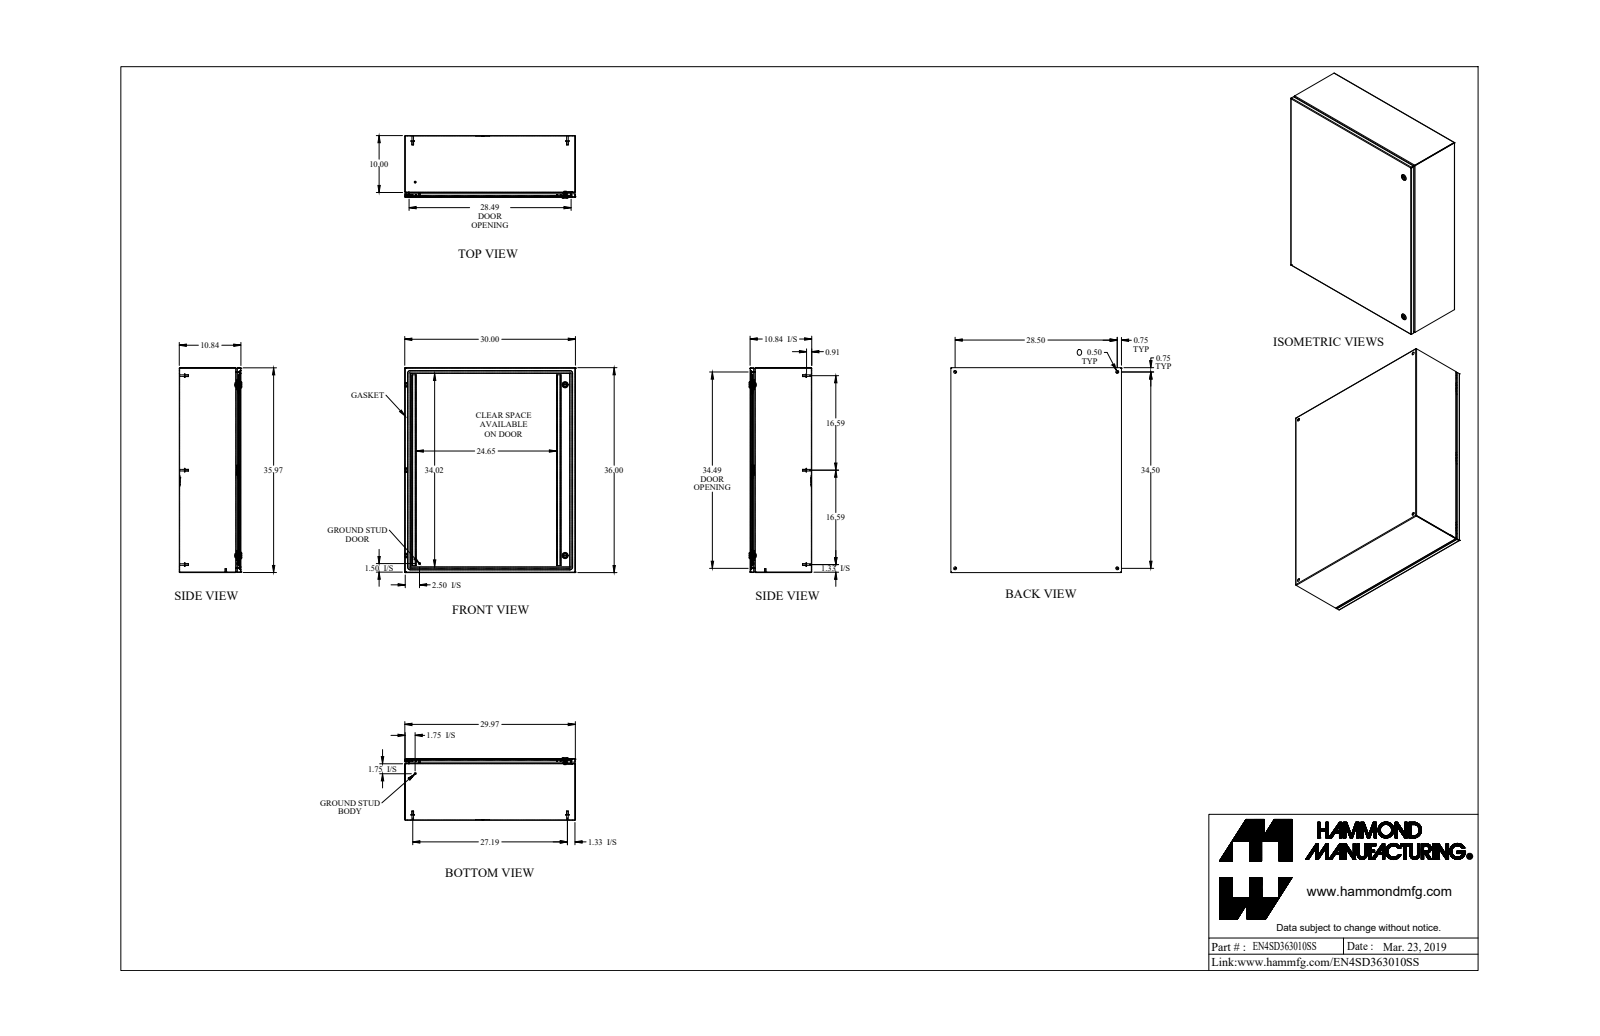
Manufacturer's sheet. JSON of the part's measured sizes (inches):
{"part_name": "EN4SD363010SS", "step_written_by": "SolidWorks 2019 (AUTOMOTIVE_DESIGN)", "units": "inches", "bodies": {"solids": 35, "faces": 959, "planar": 458, "cylindrical": 313, "other": 188}, "overall_size": [36, 30, 11.002], "volume_in3": 286.6, "surface_area_in2": 8035, "round_holes": [[0.5, 6], [0.197, 2], [0.387, 2], [0.63, 2], [0.768, 2], [0.172, 1], [0.24, 1], [0.242, 1]], "round_bosses_or_shafts": [[0.313, 8], [0.275, 6], [0.625, 4], [0.625, 4], [1.1, 2], [0.785, 2], [0.525, 2], [0.25, 2]], "partial_cylinders_radius": [[0.036, 20], [0.108, 20], [0.25, 16], [0.01, 12], [0.048, 12], [0.006, 6], [0.062, 6], [0.125, 4]], "face_to_face_distances": [0.072, 10.77, 10.698, 10.842, 29.928, 35.928, 29.856, 30, 35.856, 36], "hole_center_spacings": [2.488, 27.531, 28.5, 32.267, 34.5, 42.343, 44.749, 30]}
